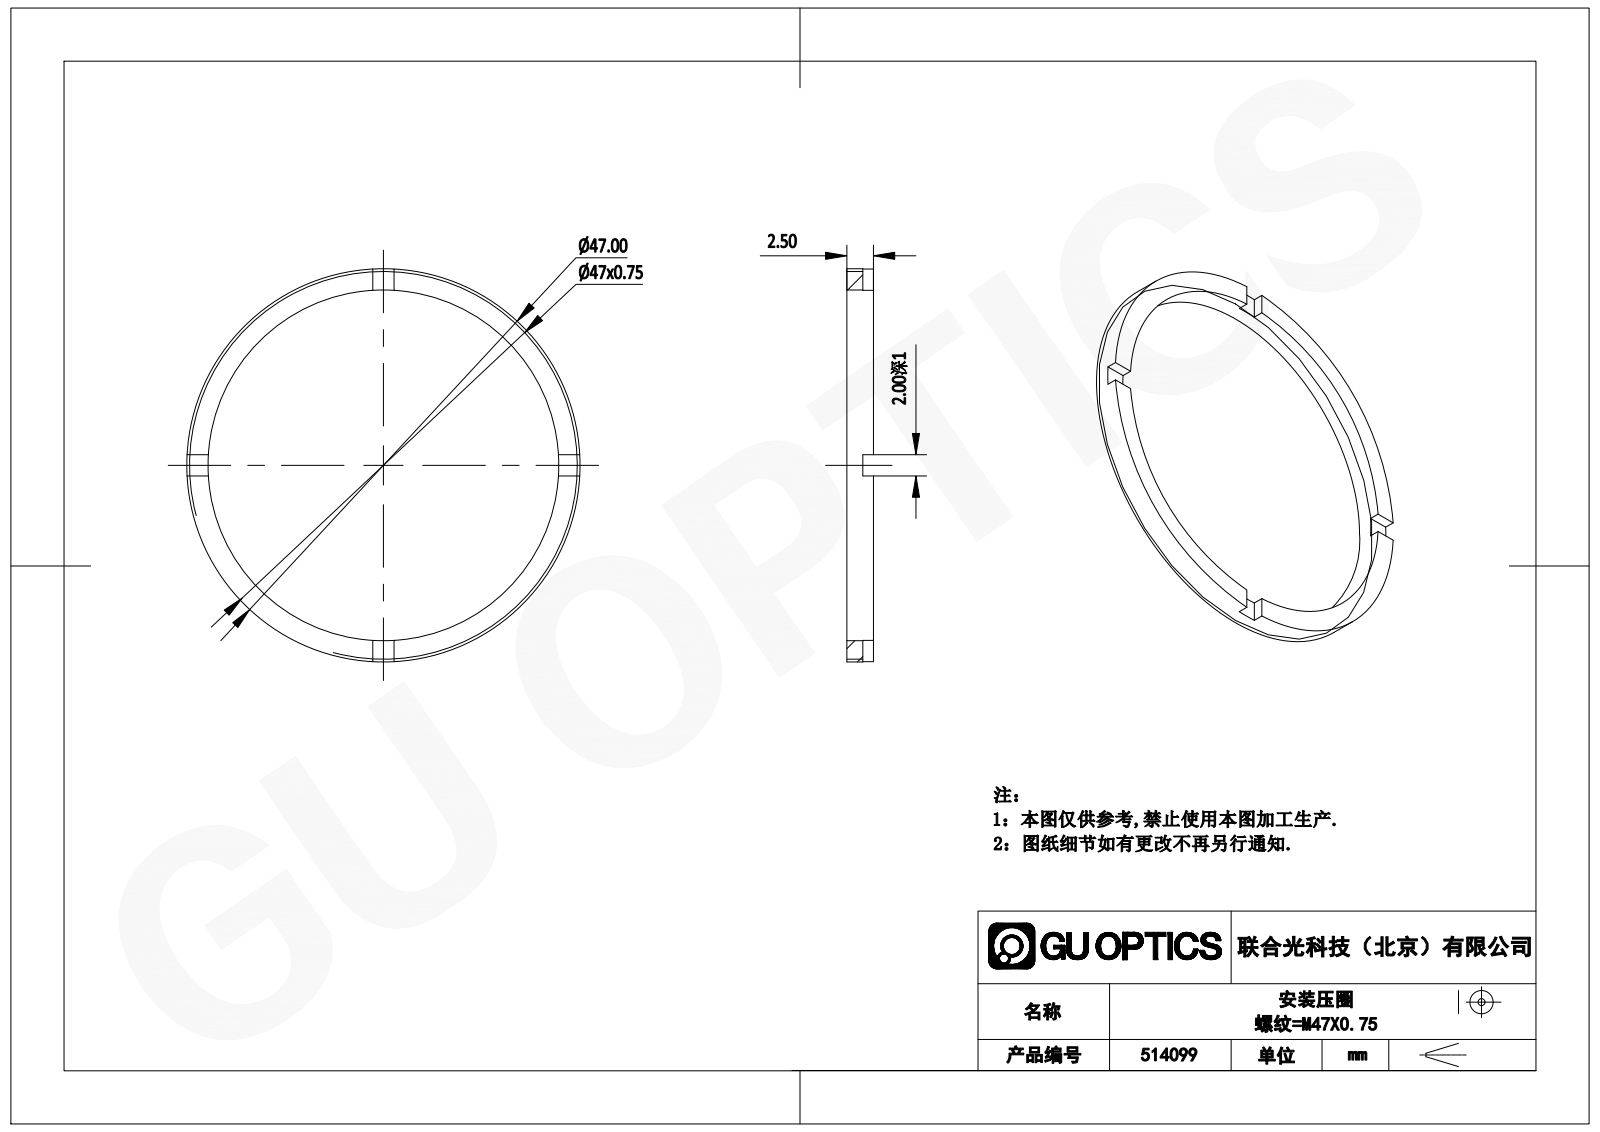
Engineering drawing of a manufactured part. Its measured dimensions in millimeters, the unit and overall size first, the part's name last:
Units: millimetres
Overall size (bounding box): 47 × 47 × 2.5
Round holes (diameter × count): ⌀43 ×1
Round bosses / shafts (diameter × count): ⌀47 ×1
Main face-to-face distances: 2.5, 1.5, 1, 2
Volume: 691 mm³ · Surface area: 1 272 mm²
Bodies: 1 solid, 21 faces (17 planar, 4 cylindrical, 0 other)
Part name (STEP PRODUCT): 514099
STEP written by: SolidWorks 2020 (CONFIG_CONTROL_DESIGN)
